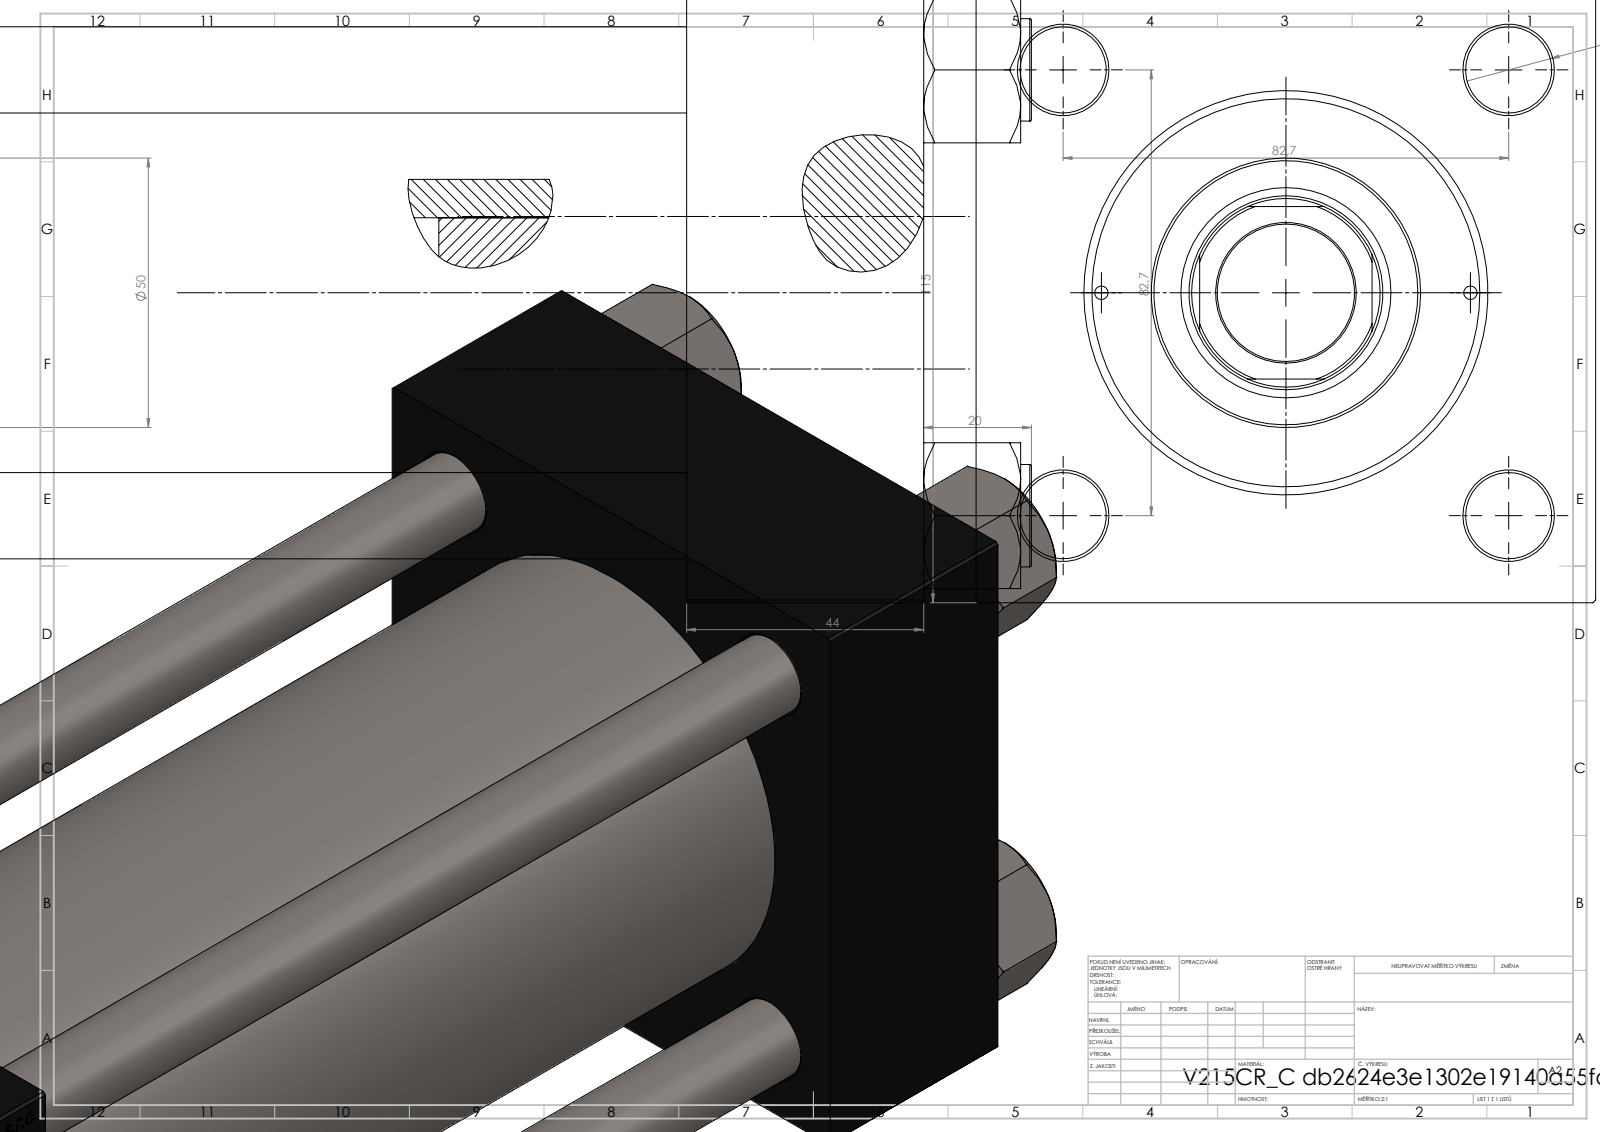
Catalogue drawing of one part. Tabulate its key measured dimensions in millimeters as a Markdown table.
| quantity | value |
| --- | --- |
| part name | V215CR_VCP_C; V215CR_C_TYCINKA; NUT_M5_C; V215_VC_A (+1 more) |
| STEP written by | SolidWorks 2019 (CONFIG_CONTROL_DESIGN) |
| units | millimeters |
| bodies | 11 solids, 1203 faces (576 planar, 91 cylindrical, 536 other) |
| overall size | 370 × 115 × 115 |
| volume | 2 151 000 mm³ |
| surface area | 385 507 mm² |
| round holes (diameter × count) | 16 × 4, 2.5 × 2, 7 × 2, 26.44 × 2, 35 × 2, 25.5 × 1, 36 × 1, 39 × 1, 61 × 1, 72 × 1, 80 × 1 |
| round bosses / shafts (diameter × count) | 19 × 4, 86 × 1, 50 × 1 |
| partial cylindrical surfaces (radius × count) | 17.5 × 1 |
| main face-to-face distances | 115, 44, 319, 275, 69, 250, 206, 290.3, 246.3, 40.3 |
| hole center spacings | 41.96, 58.48, 82.7, 86.17, 34.25, 116.96, 68.5, 251 |
